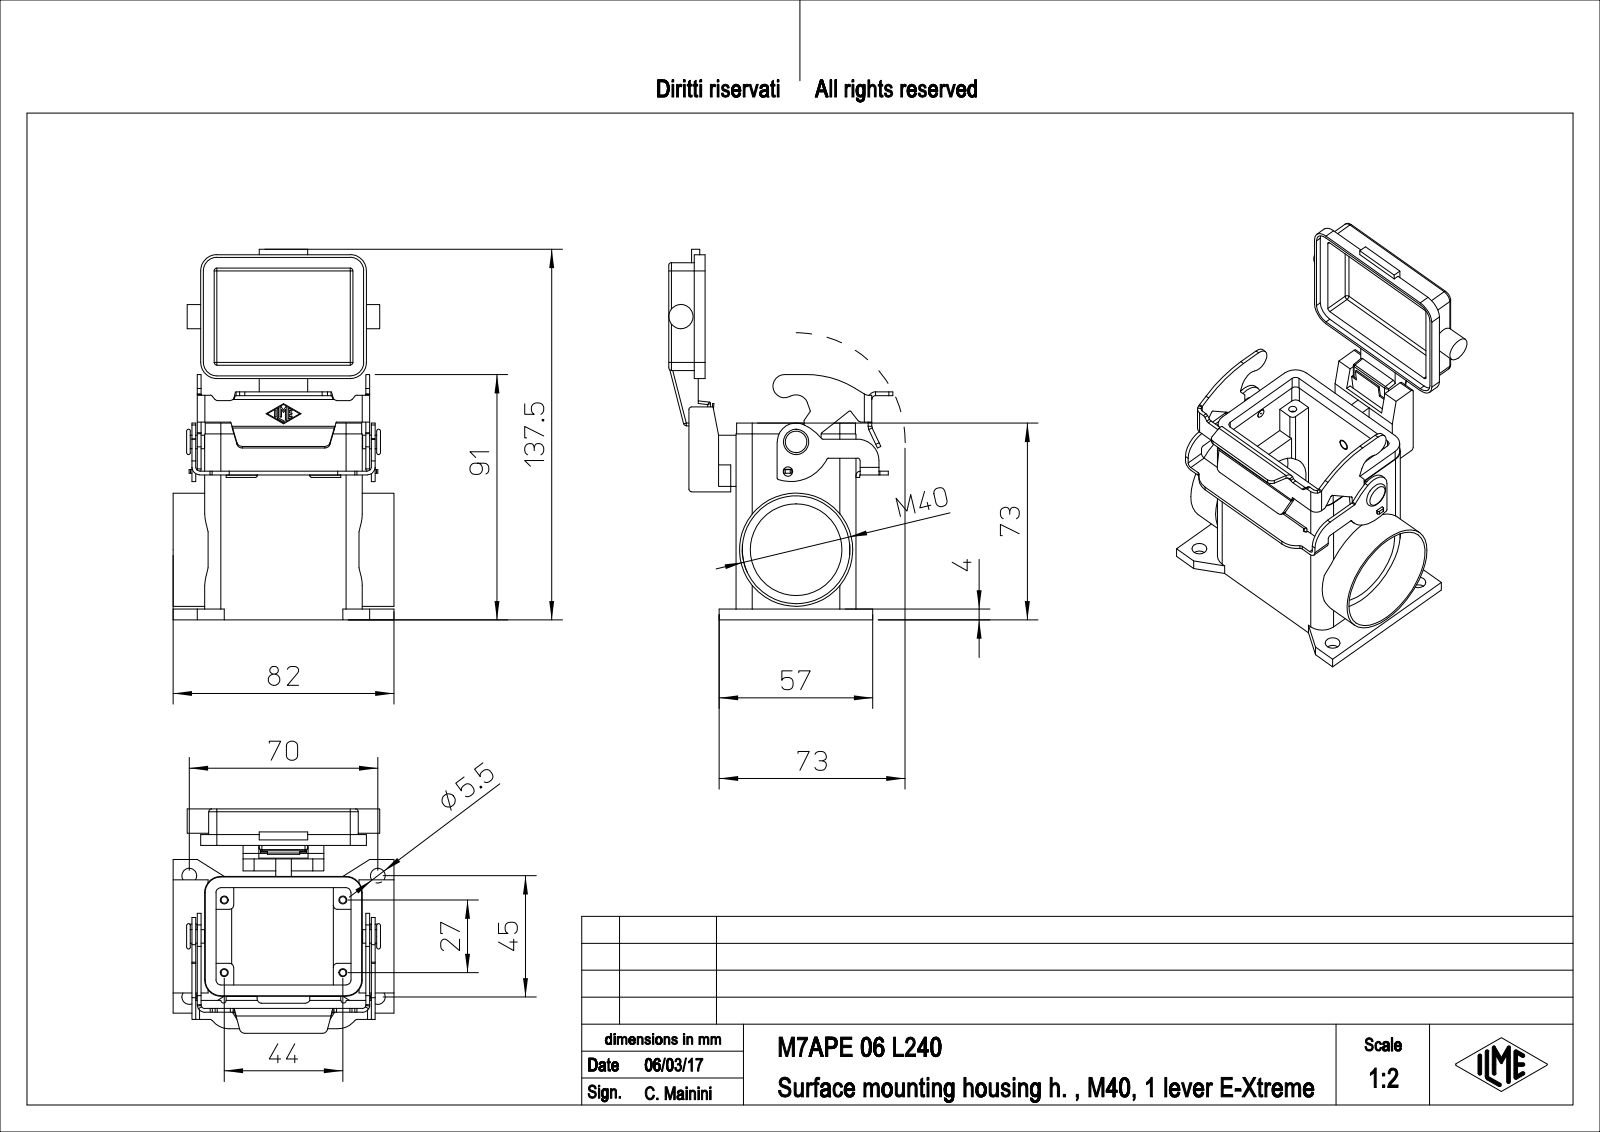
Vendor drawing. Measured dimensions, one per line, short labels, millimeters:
name: M7APE_06_L240
written by: PTC Creo Elements/Direct Modeling 19.0E 27-Jun-2016 (C) Parametric Technology GmbH (AUTOMOTIVE_DESIGN)
unit: mm
bodies: 2 solids, 570 faces (297 planar, 233 cylindrical, 40 other)
size: 137.5 × 83.23 × 82
holes: 4× ⌀2.46, 4× ⌀3, 4× ⌀5.5, 1× ⌀3.5, 1× ⌀4, 1× ⌀34, 1× ⌀40
bosses: 1× ⌀42, 1× ⌀9, 1× ⌀7, 1× ⌀5, 1× ⌀3.2, 1× ⌀3
rounds: 36× R1, 16× R0.25, 13× R0.5, 11× R1.5, 9× R2, 8× R6, 6× R1.4, 6× R2.8
face distances: 4, 40.5, 2, 1.4, 44.5, 13.5, 36.5, 68, 64, 69.5
hole spacings: 15.81, 38.28, 57.71, 67.42, 27, 44, 45, 51.62
